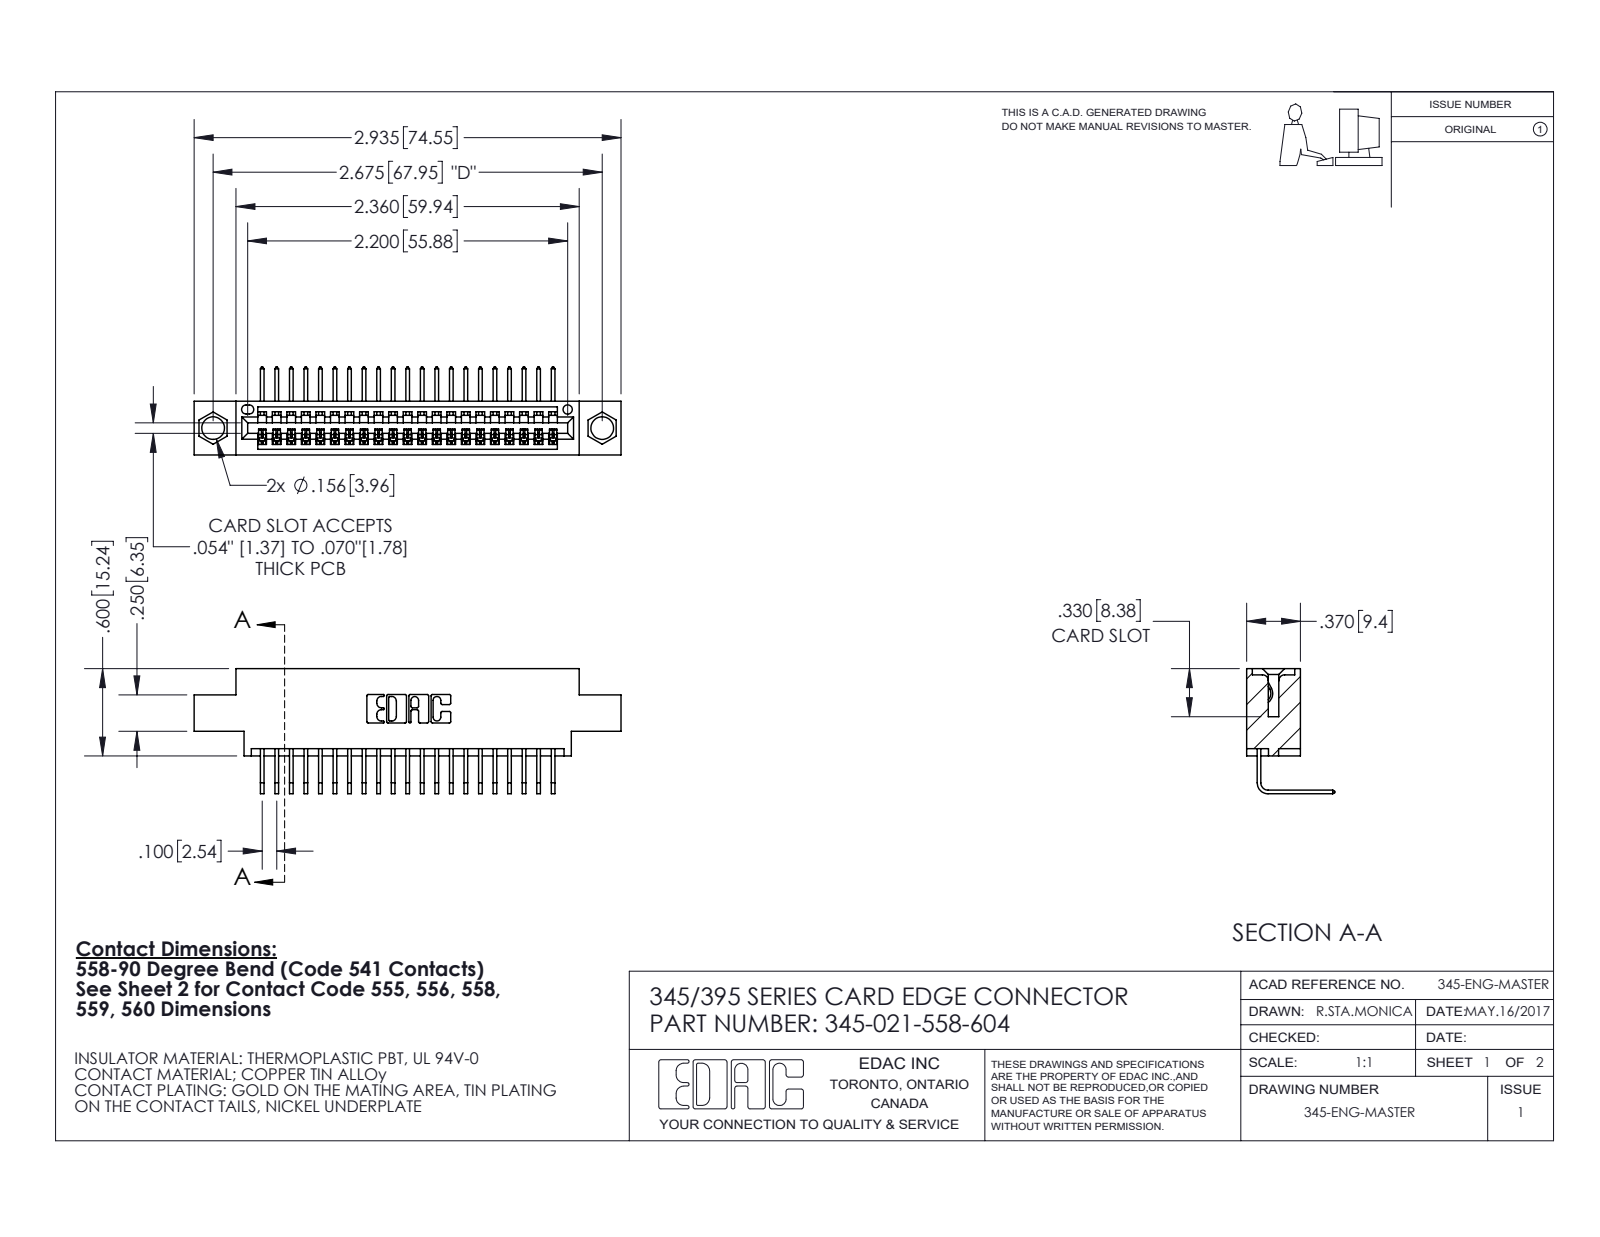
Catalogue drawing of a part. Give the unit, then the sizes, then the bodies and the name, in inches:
Units: inches
Overall size (bounding box): 2.935 × 0.859 × 0.605
Round holes (diameter × count): ⌀0.156 ×2, ⌀0.064 ×1
Partial cylindrical surfaces — rounded edges, fillets, slot ends (radius × count): R0.006 ×42, R0.01 ×22, R0.007 ×6, R0.031 ×6, R0.026 ×3, R0.031 ×2, R0.04 ×2, R0.014 ×1
Main face-to-face distances: 0.072, 0.298, 0.37, 0.2, 0.098, 0.272, 0.025, 0.225, 0.175, 0.149
Hole centre spacings: 0.27, 2.441, 2.675
Volume: 0.412 in³ · Surface area: 14.07 in²
Bodies: 22 solids, 1404 faces (980 planar, 424 cylindrical, 0 other)
Part name (STEP PRODUCT): 345-021-558-604; 345 Part_0.170 Offset - 0.156 Dia-TI; 345-292-001_558 Tail - 2
STEP written by: SolidWorks 2020 (CONFIG_CONTROL_DESIGN)
